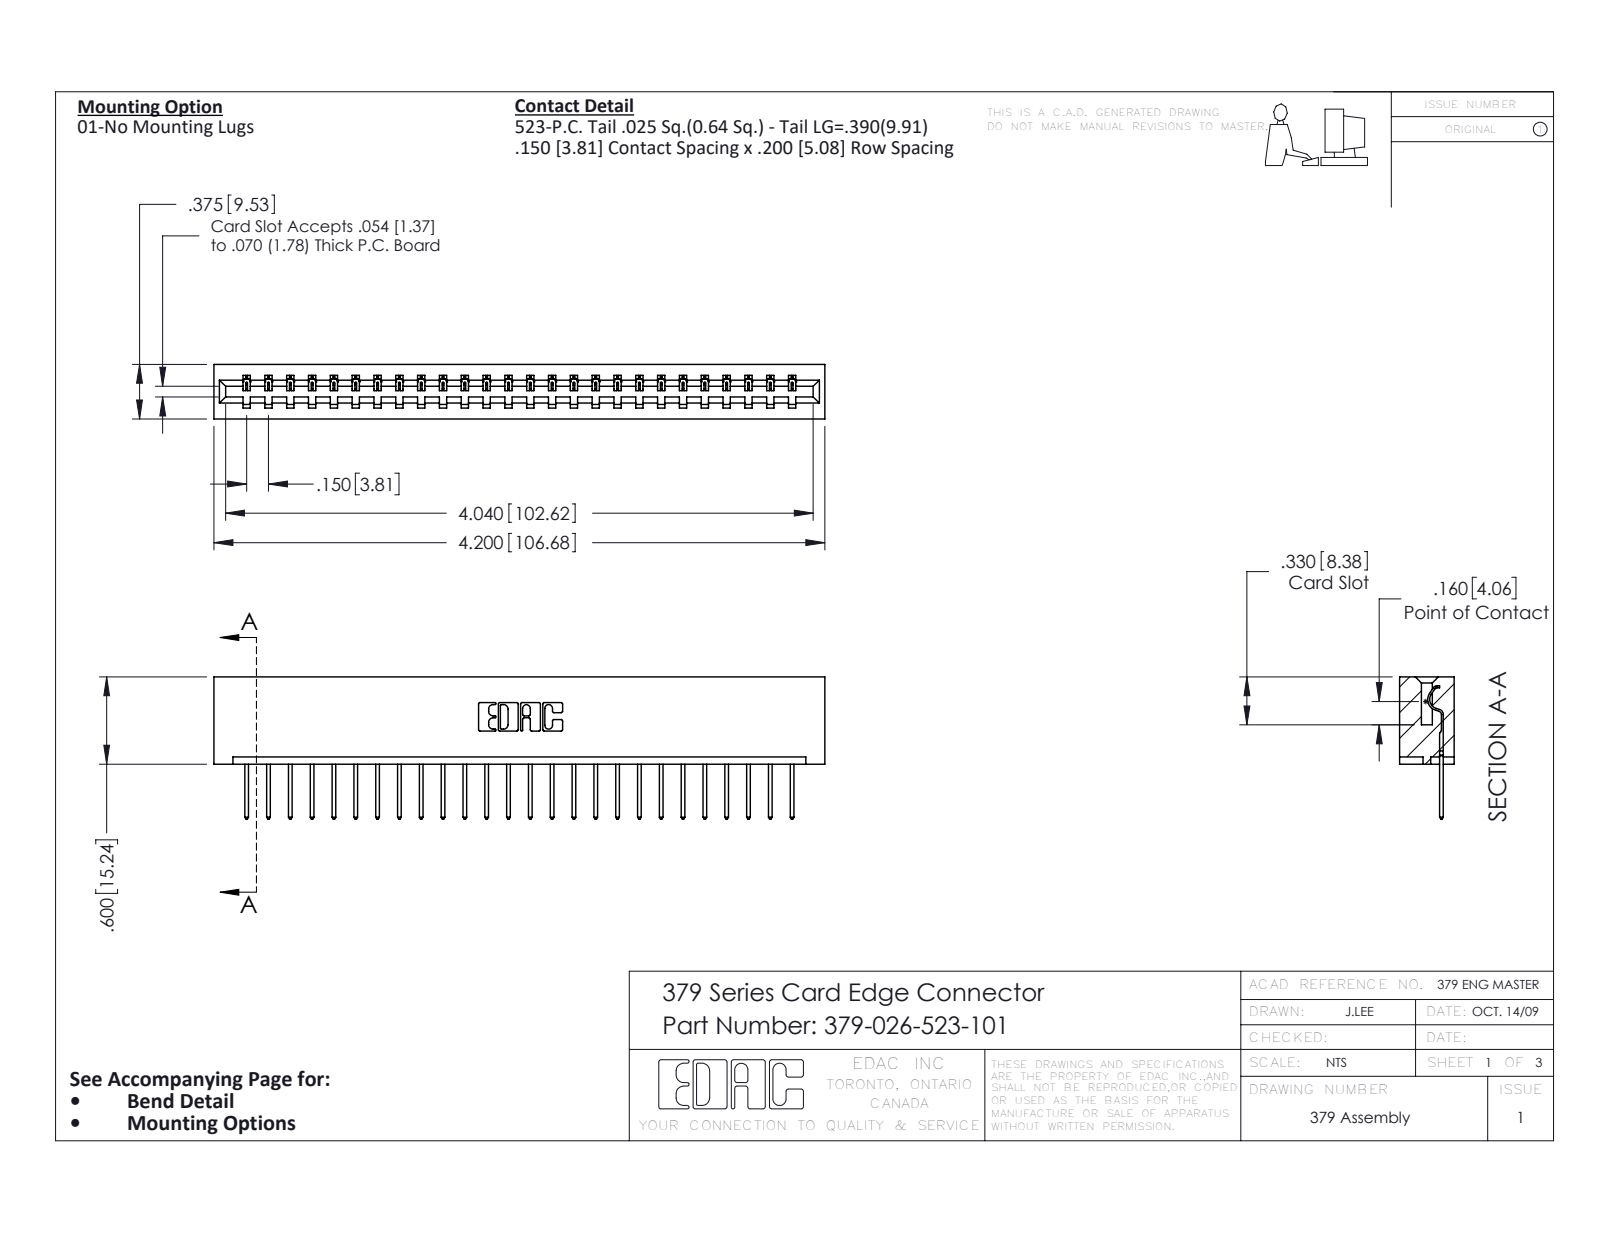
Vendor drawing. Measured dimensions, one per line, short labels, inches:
name: 345-292-001_345-293-123; 379 Part_Lugless; 379-026-523-101
written by: SolidWorks 2016 (CONFIG_CONTROL_DESIGN)
unit: in
bodies: 27 solids, 1614 faces (1158 planar, 456 cylindrical, 0 other)
size: 4.2 × 0.977 × 0.375
volume: 0.716 in³; area: 18.46 in²
rounds: 52× R0.006, 52× R0.01, 22× R0.01, 6× R0.007, 6× R0.031, 3× R0.026, 1× R0.014, 1× R0.022
face distances: 0.3, 0.075, 0.375, 0.225, 0.6, 0.15, 0.1, 0.275, 0.025, 0.45
